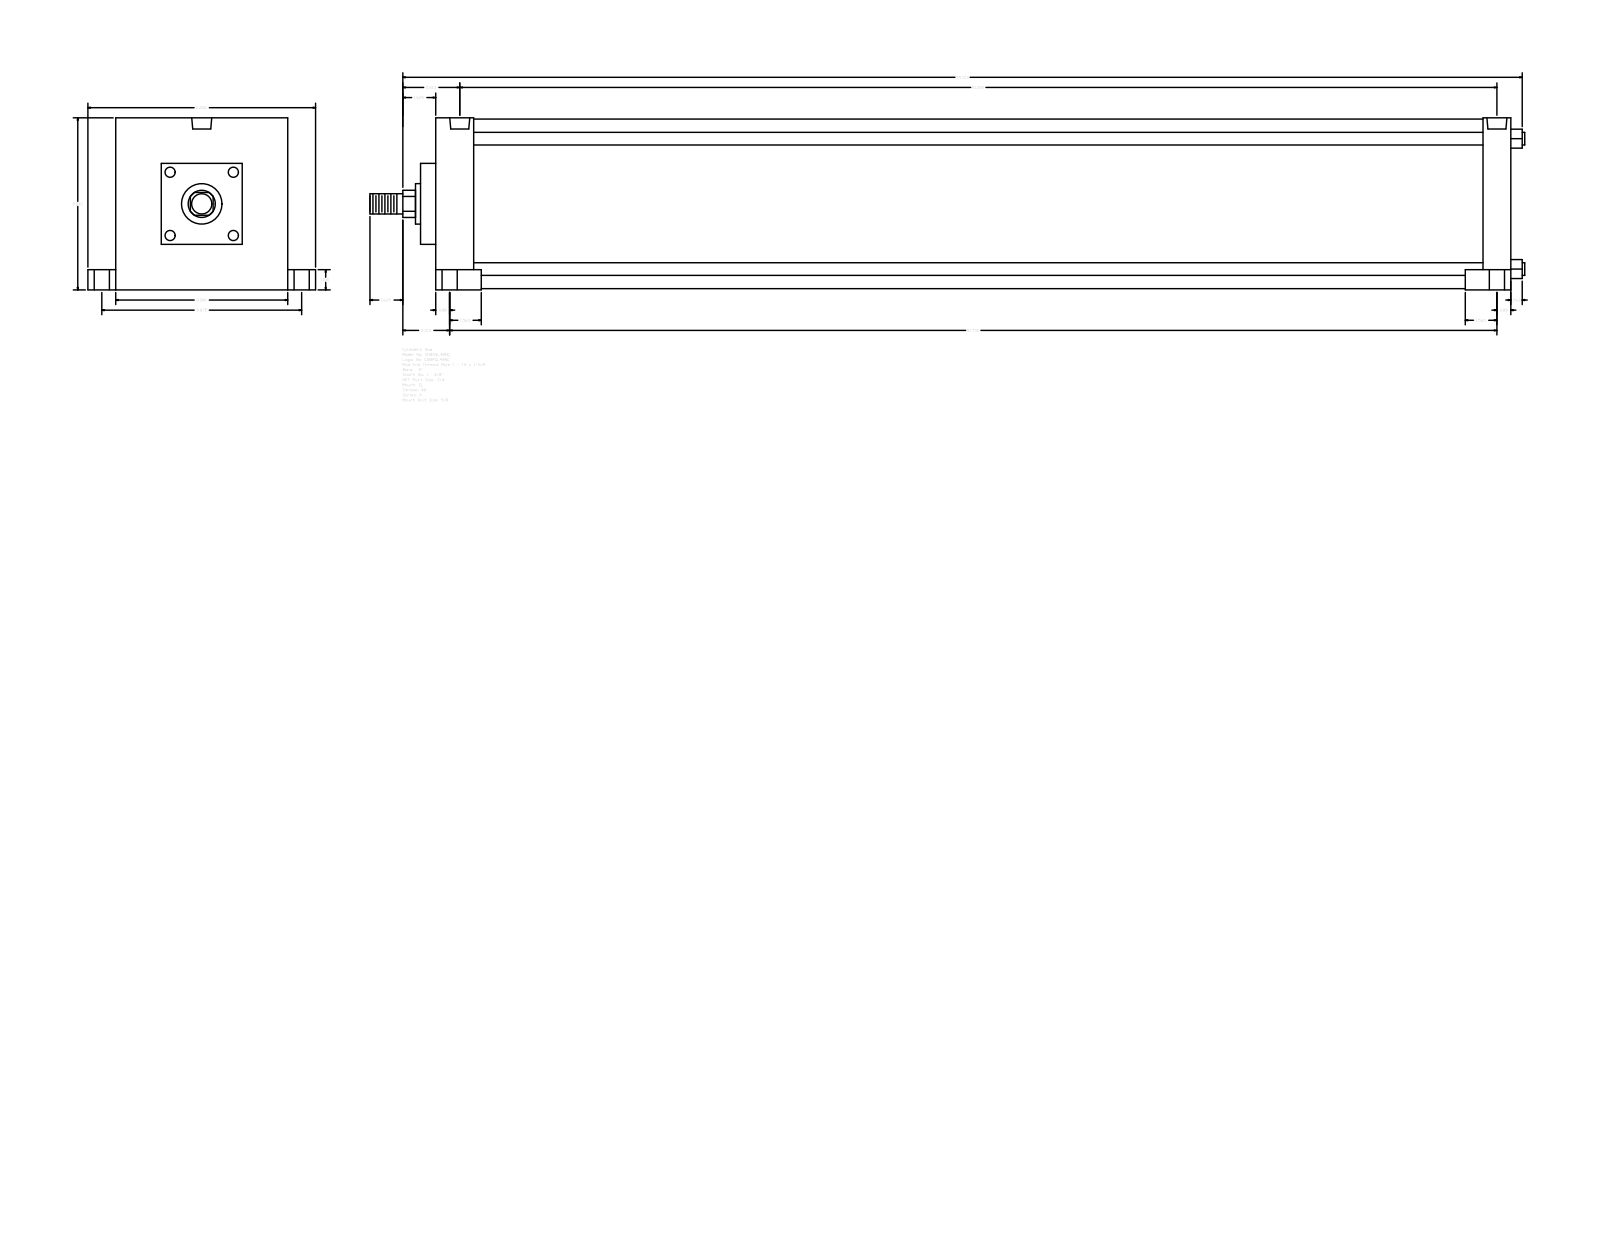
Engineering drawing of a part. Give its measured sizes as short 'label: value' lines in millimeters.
name: A_SL__0800_1.375
written by: GSSL Pune (CONFIG_CONTROL_DESIGN)
unit: mm
bodies: 0 solids, 117 faces (85 planar, 32 cylindrical, 0 other)
size: 1449.39 × 285.75 × 215.9
holes: 4× ⌀15.08, 4× ⌀19.05, 4× ⌀25.4, 2× ⌀25.12
bosses: 4× ⌀15.88, 1× ⌀212.72, 1× ⌀50.8, 1× ⌀34.92, 1× ⌀25.4
rounds: 1× R17.06
face distances: 1349.38, 215.9, 34.93, 57.15, 47.63, 1301.75, 1314.45, 1266.82, 19.04, 66.67
hole spacings: 6.35, 125.41, 125.57, 126.05, 126.85, 250.82, 1289.05, 1295.4
